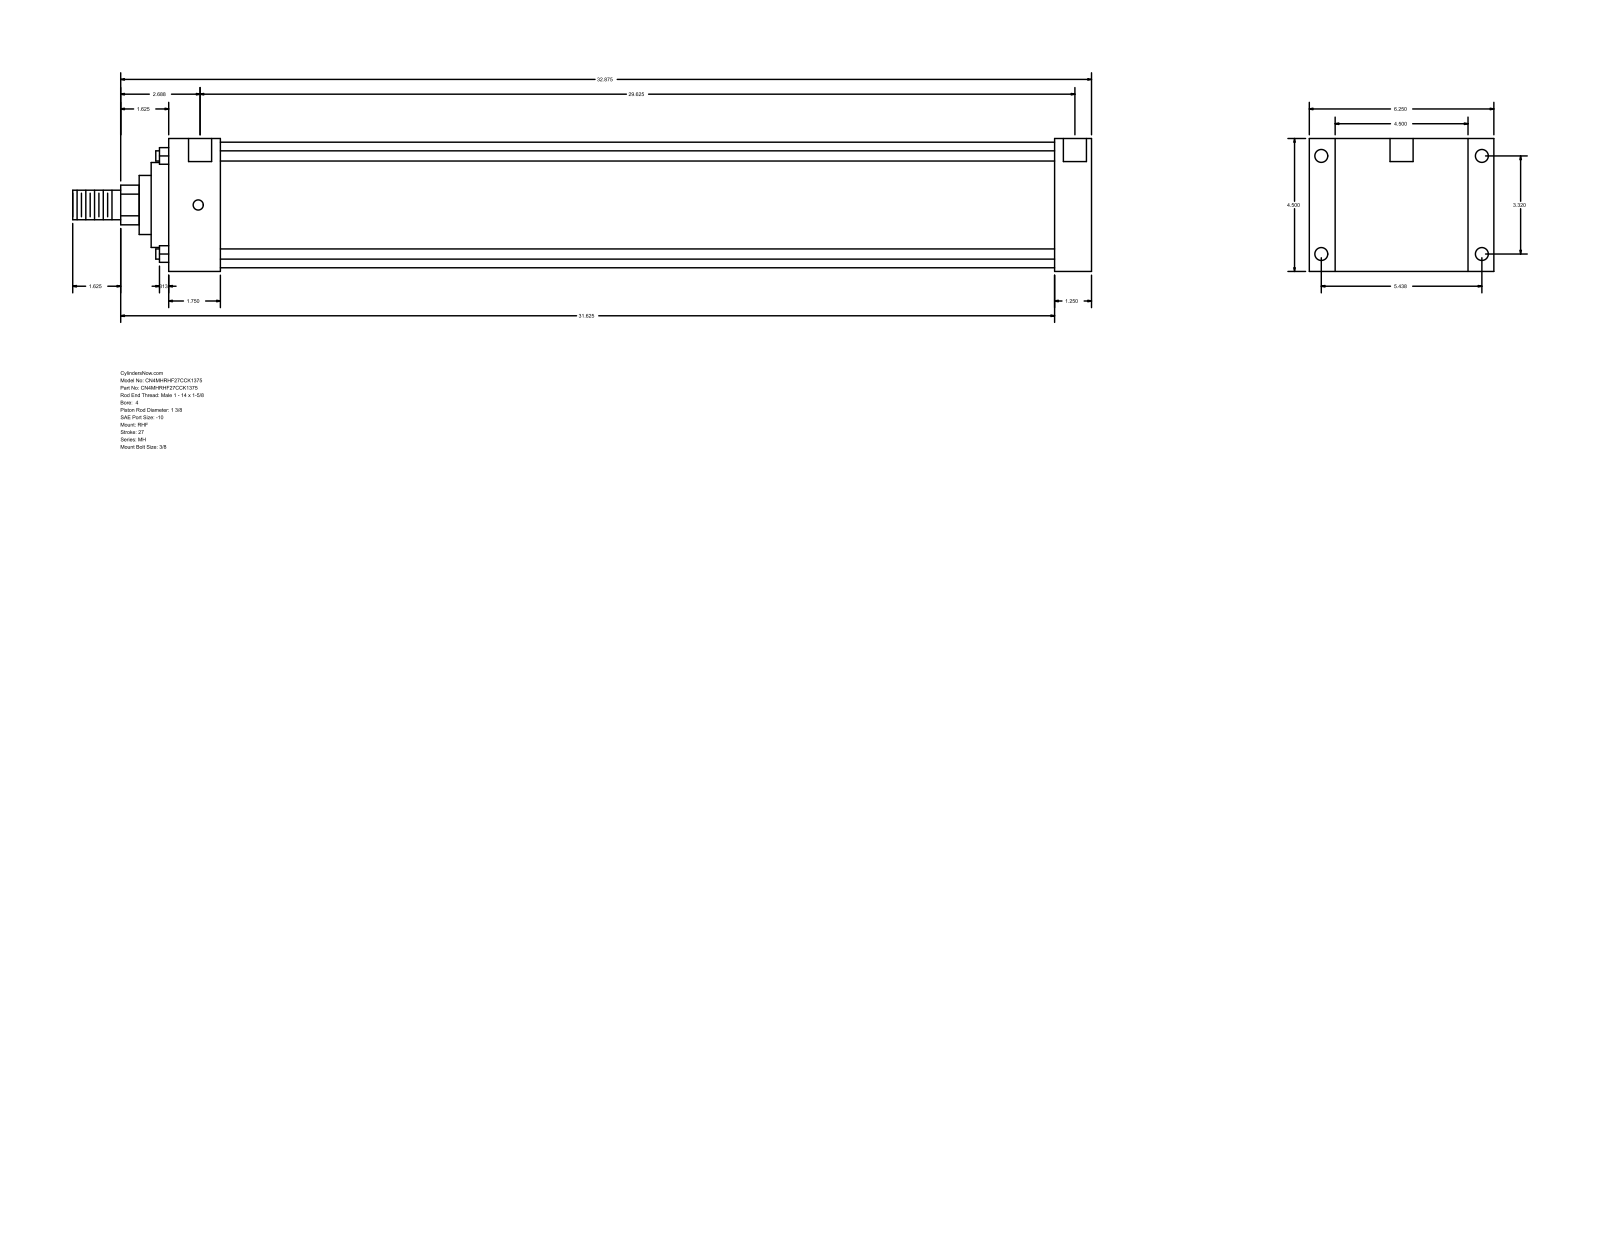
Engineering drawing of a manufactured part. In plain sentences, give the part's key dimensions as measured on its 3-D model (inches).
The part is named "MH_RHF__0400_1.375". Its 3-D file was written by "GSSL Pune (CONFIG_CONTROL_DESIGN)". It is 0 solids with 90 faces: 61 planar, 29 cylindrical and 0 other. Overall it measures 34.5 by 6.25 by 4.5 inches. Round holes: 4 of diameter 0.344, 4 of diameter 0.438, 2 of diameter 0.781. Round bosses or shafts: 4 of diameter 0.345, 1 of diameter 4.25, 1 of diameter 2.875, 1 of diameter 2, 1 of diameter 1.375, 1 of diameter 1. Partial cylindrical surfaces (rounded edges, fillets, slot ends): 1 of radius 0.672. The main face-to-face distances are 4.5, 1.25, 30, 31.25, 0.875, 5.375, 1.75, 28.25, 29.5, 6.25. The hole center spacings are 0.063, 3.32, 5.438, 6.371, 29.688, 29.75, 29.625.
